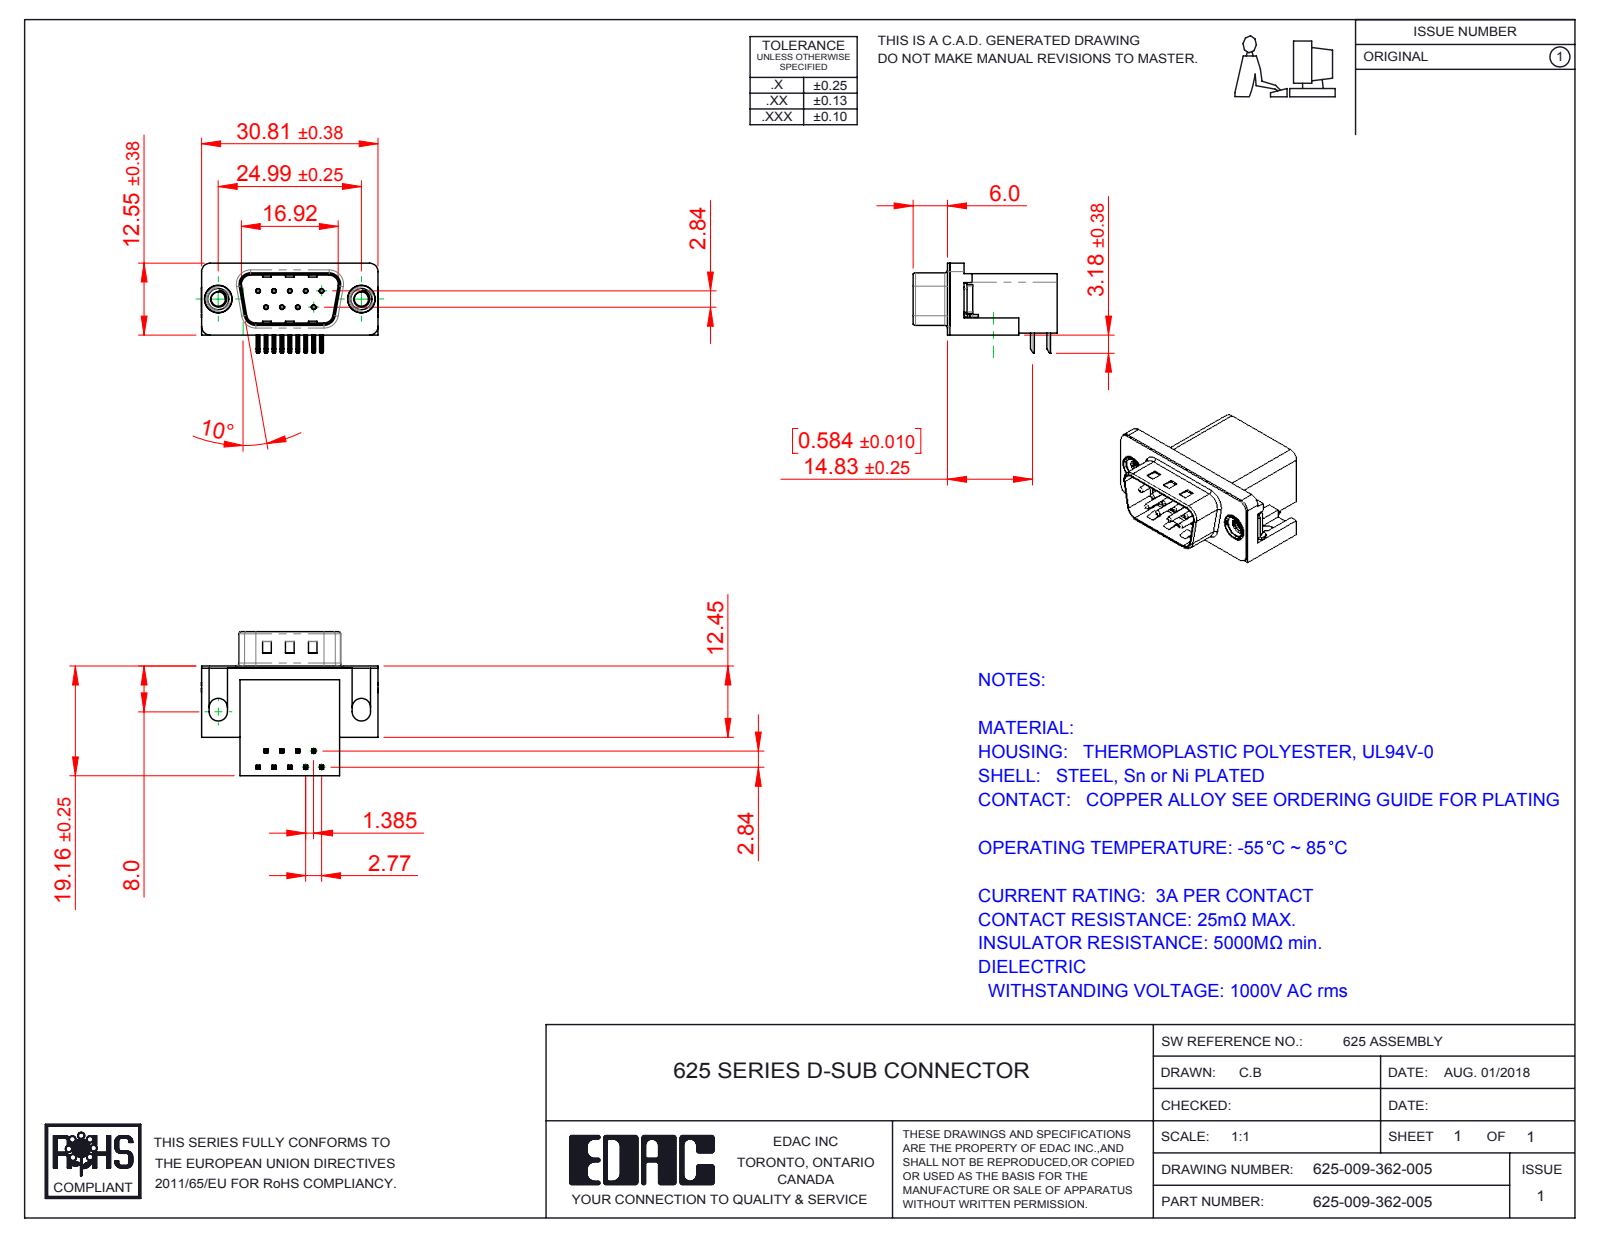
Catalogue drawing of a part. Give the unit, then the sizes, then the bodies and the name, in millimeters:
Units: millimetres
Overall size (bounding box): 30.89 × 25.16 × 15.73
Round holes (diameter × count): ⌀0.35 ×9, ⌀0.8 ×9, ⌀2.5 ×2, ⌀4 ×2, ⌀4.8 ×2, ⌀5 ×2
Round bosses / shafts (diameter × count): ⌀0.75 ×9, ⌀4.9 ×2, ⌀4.75 ×2, ⌀3.9 ×2
Partial cylindrical surfaces — rounded edges, fillets, slot ends (radius × count): R0.25 ×44, R0.12 ×18, R1 ×16, R0.5 ×9, R1.5 ×8, R1.6 ×8, R0.9 ×4, R2 ×4
Main face-to-face distances: 0.4, 10.34, 18.76, 19.16, 2.9, 16.26, 2.5, 0.35, 10.69, 6.7
Hole centre spacings: 3.16, 2.77, 5.54, 5.03, 5.04, 8.31, 7.48, 7.49
Volume: 4 442 mm³ · Surface area: 4 821 mm²
Bodies: 15 solids, 991 faces (575 planar, 317 cylindrical, 99 other)
Part name (STEP PRODUCT): 625 Contact Bottom; 625 Contact Top; 625 Non Board Mount; 625 Housing_9 Socket (+3 more)
STEP written by: SolidWorks 2016 (CONFIG_CONTROL_DESIGN)
